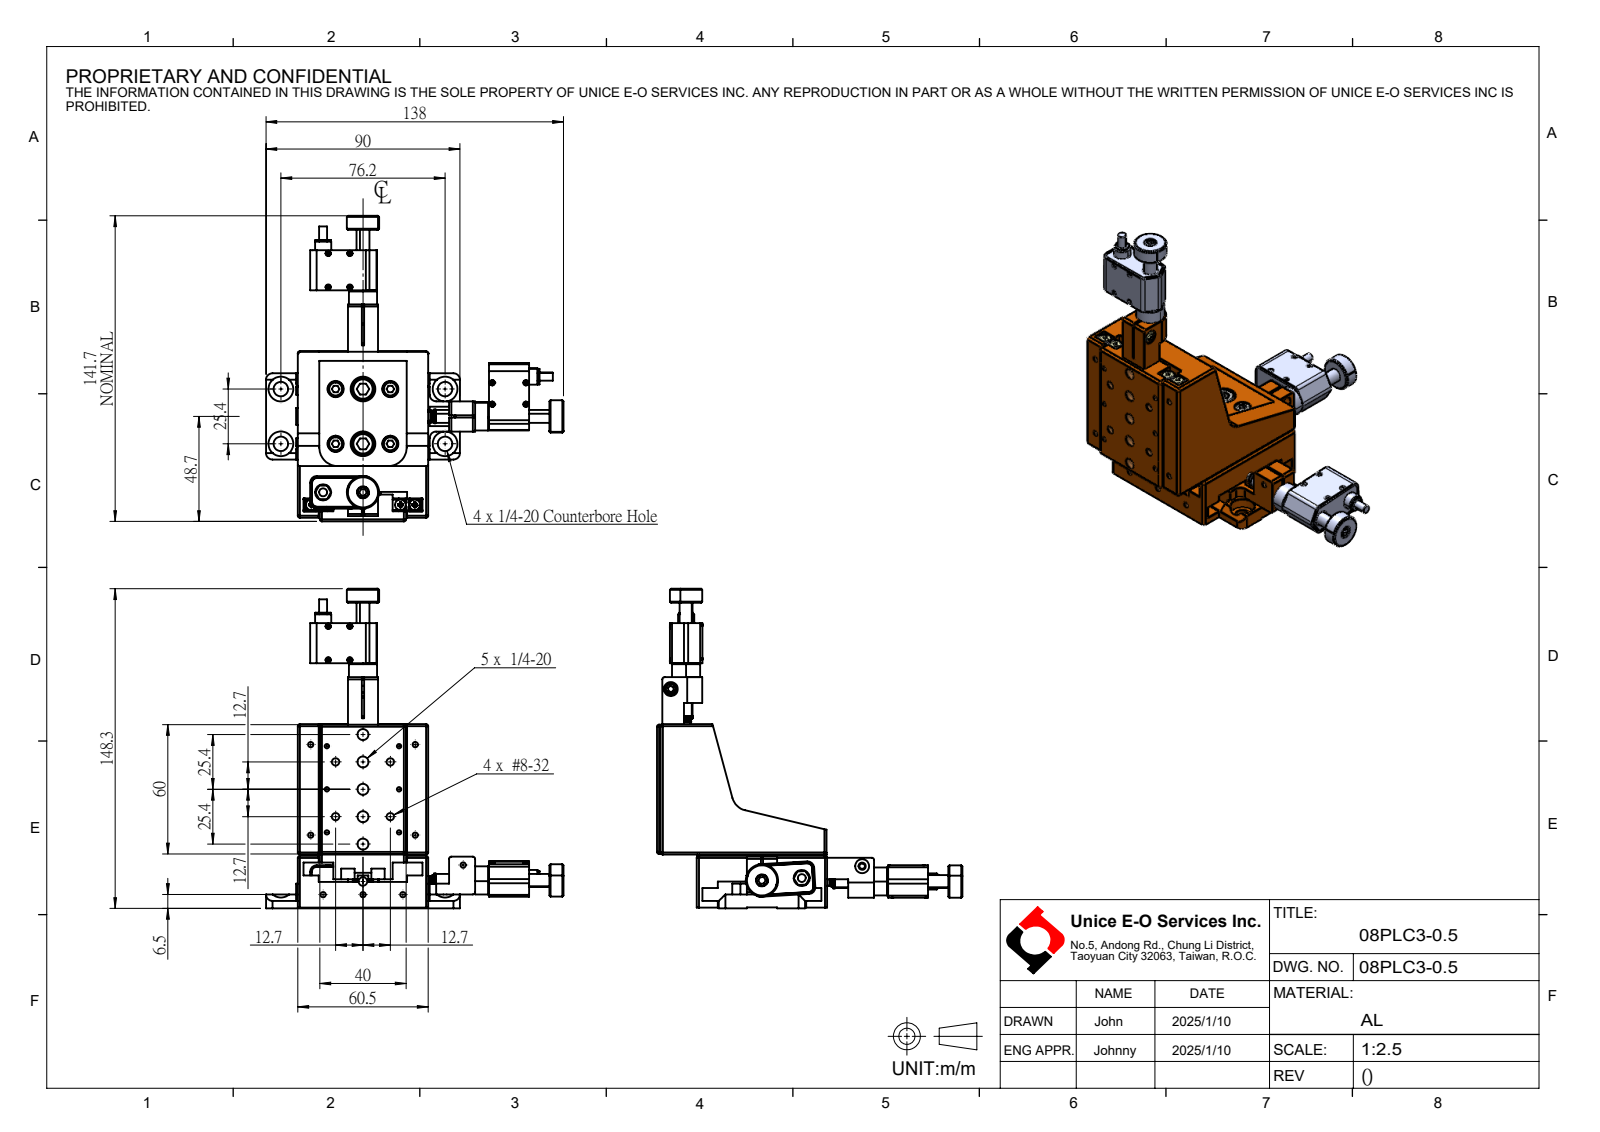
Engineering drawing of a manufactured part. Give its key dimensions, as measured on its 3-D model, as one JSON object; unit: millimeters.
{"part_name": "08PLC3-0.5", "step_written_by": "SolidWorks 2024 (CONFIG_CONTROL_DESIGN)", "units": "millimeters", "bodies": {"solids": 0, "faces": 1058, "planar": 548, "cylindrical": 348, "other": 162}, "overall_size": [148.27, 141.72, 138.02], "round_holes": [[2.5, 29], [2.05, 12], [11.51, 6], [5.11, 5], [3.45, 4], [6.76, 4], [7.54, 4], [2, 3], [5.6, 3], [6.5, 3], [7.5, 3], [9.5, 3]], "round_bosses_or_shafts": [[5, 6], [2, 6], [15, 3], [6.4, 3], [6, 3], [4, 3], [3.7, 3], [10, 2]], "partial_cylinders_radius": [[1, 43], [3, 12], [2, 10], [7, 2], [8.5, 2], [0.7, 1], [1.5, 1], [2.5, 1]], "face_to_face_distances": [3, 6, 60.5, 9, 12.5, 3.1, 16.5, 12, 13.5, 6.75], "hole_center_spacings": [25.4, 12.7, 8.35, 13.33, 14.22, 17.96, 18.5, 20]}
